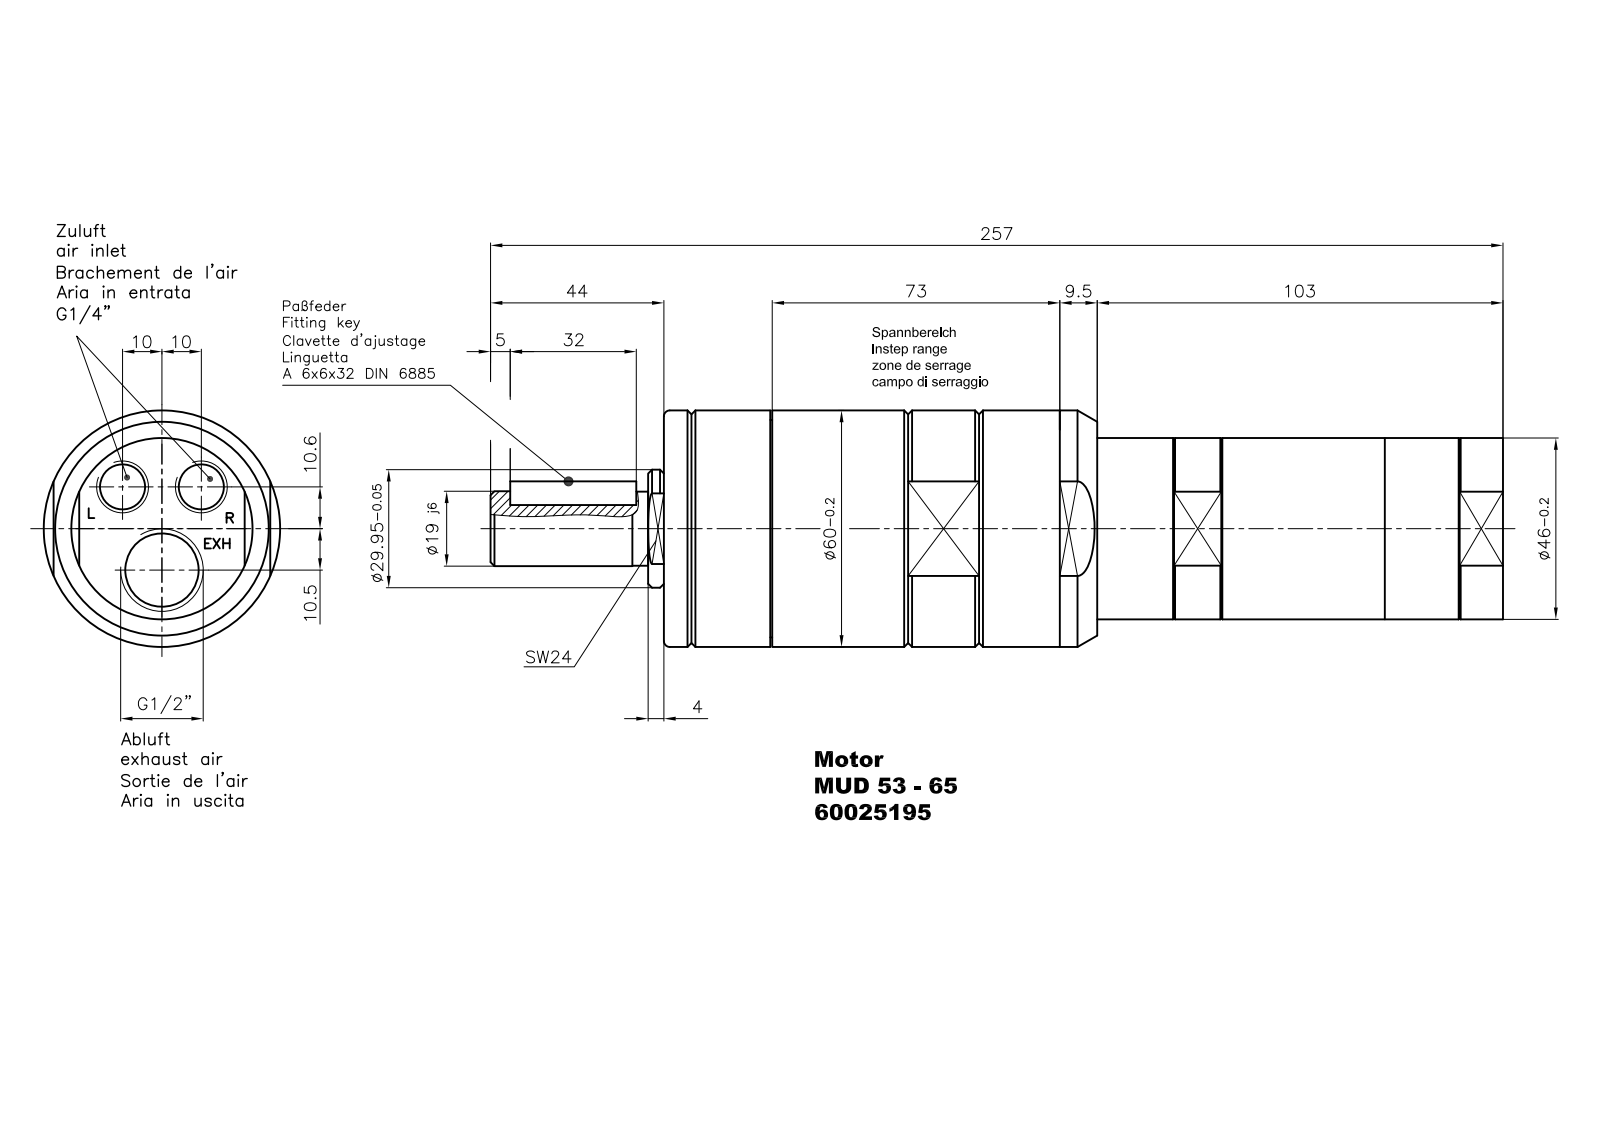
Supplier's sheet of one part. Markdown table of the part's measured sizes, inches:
| quantity | value |
| --- | --- |
| part name | MUD 53-257 |
| STEP written by | Autodesk Inventor 2012 (AUTOMOTIVE_DESIGN) |
| units | inches |
| bodies | 1 solid, 179 faces (104 planar, 35 cylindrical, 40 other) |
| overall size | 10.118 × 2.362 × 2.362 |
| volume | 29.5 in³ |
| surface area | 79.66 in² |
| round holes (diameter × count) | 0.451 × 2, 0.061 × 1, 0.063 × 1, 0.217 × 1, 0.733 × 1, 0.787 × 1, 1.378 × 1, 1.831 × 1 |
| round bosses / shafts (diameter × count) | 2.362 × 1, 2.172 × 1, 1.811 × 1, 1.179 × 1, 0.748 × 1, 0.74 × 1, 0.197 × 1 |
| partial cylindrical surfaces (radius × count) | 0.118 × 2 |
| main face-to-face distances | 3.957, 2.874, 3.248, 8.386, 4.429, 0.256, 4.055, 2.165, 4.331, 0.374 |
| hole center spacings | 0.574, 0.919, 0.413, 0.787 |
